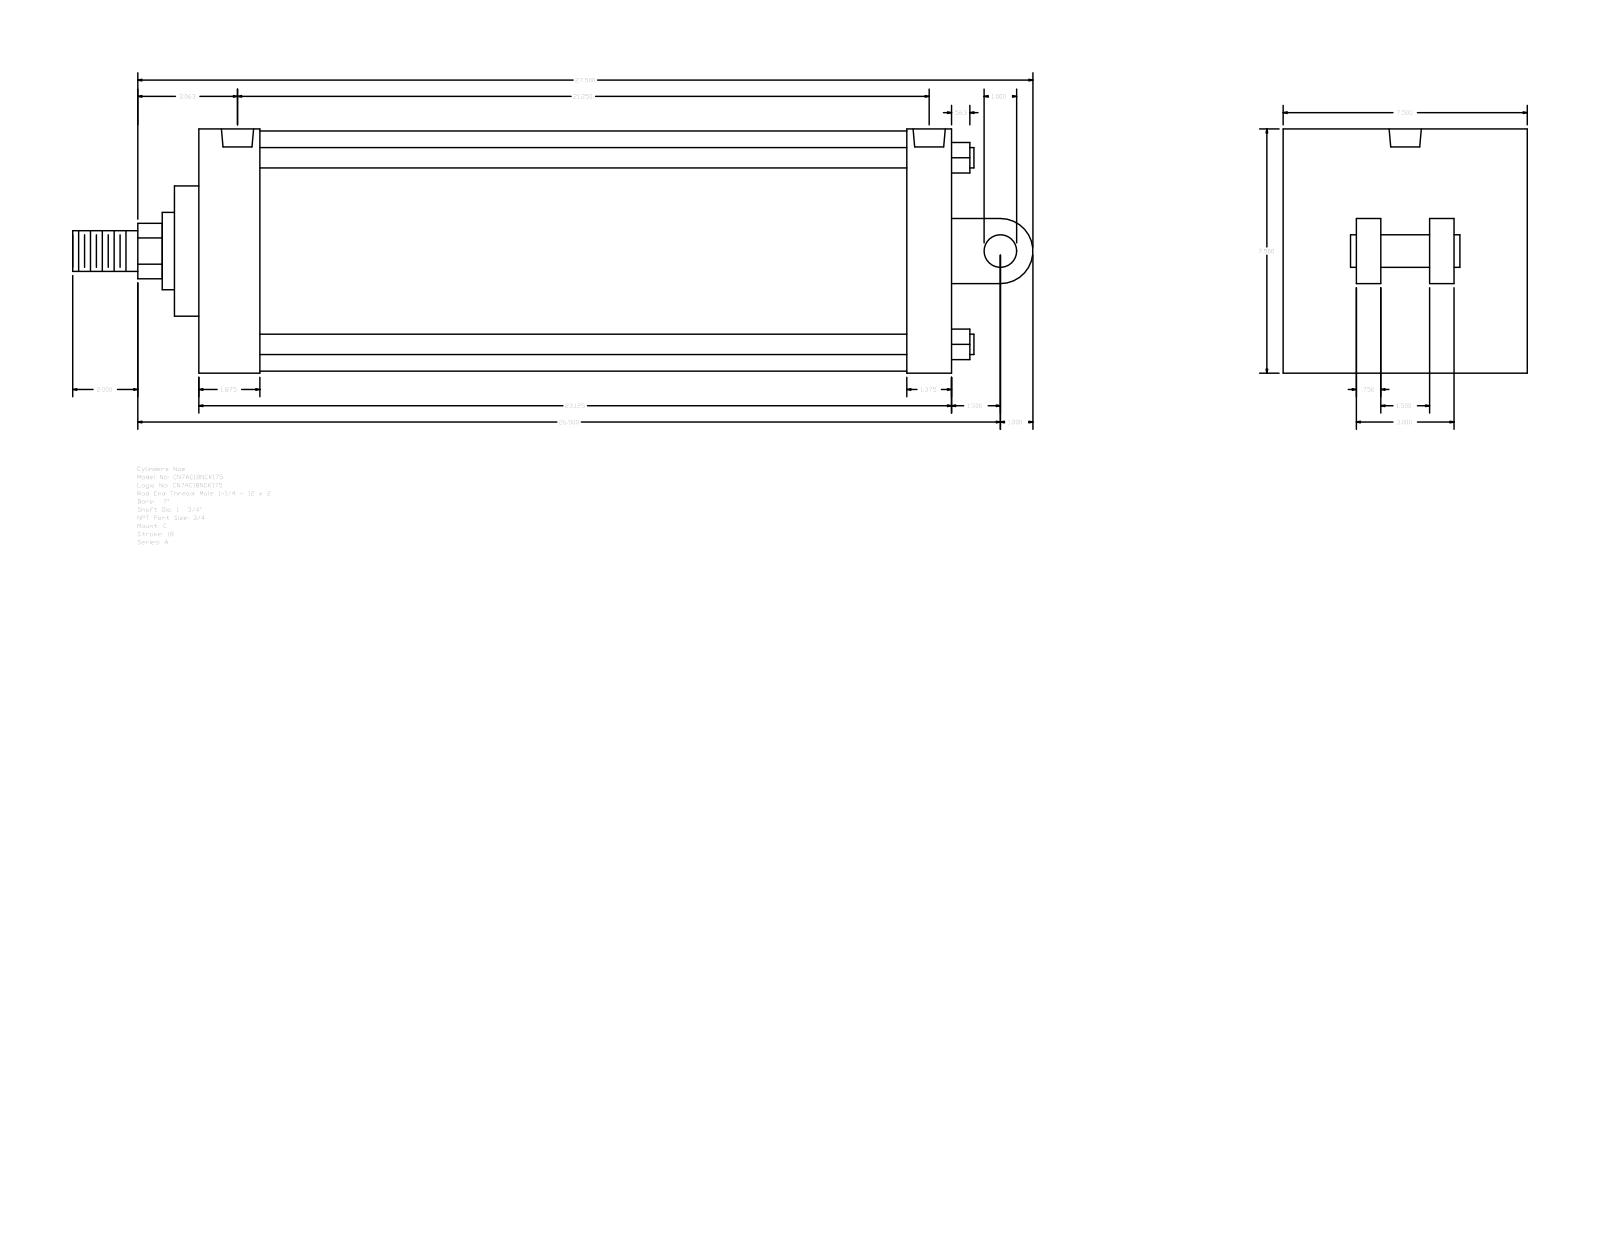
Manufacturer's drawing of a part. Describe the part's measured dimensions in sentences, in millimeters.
The part is named "A_C__0700_1.75". Its 3-D file was written by "GSSL Pune (CONFIG_CONTROL_DESIGN)". It is 0 solids with 104 faces: 75 planar, 29 cylindrical and 0 other. Overall it measures 749.3 by 190.5 by 190.5 millimeters. Round holes: 4 of diameter 15.08, 2 of diameter 25.12. Round bosses or shafts: 4 of diameter 15.88, 1 of diameter 187.32, 1 of diameter 60.33, 1 of diameter 44.45, 1 of diameter 31.75, 1 of diameter 25.4. Partial cylindrical surfaces (rounded edges, fillets, slot ends): 1 of radius 21.63, 1 of radius 25.4. The main face-to-face distances are 190.5, 587.38, 19.05, 76.2, 57.15, 146.05, 44.45, 69.85, 47.63, 539.75. The hole center spacings are 5.56, 528.63, 534.19, 539.75.
